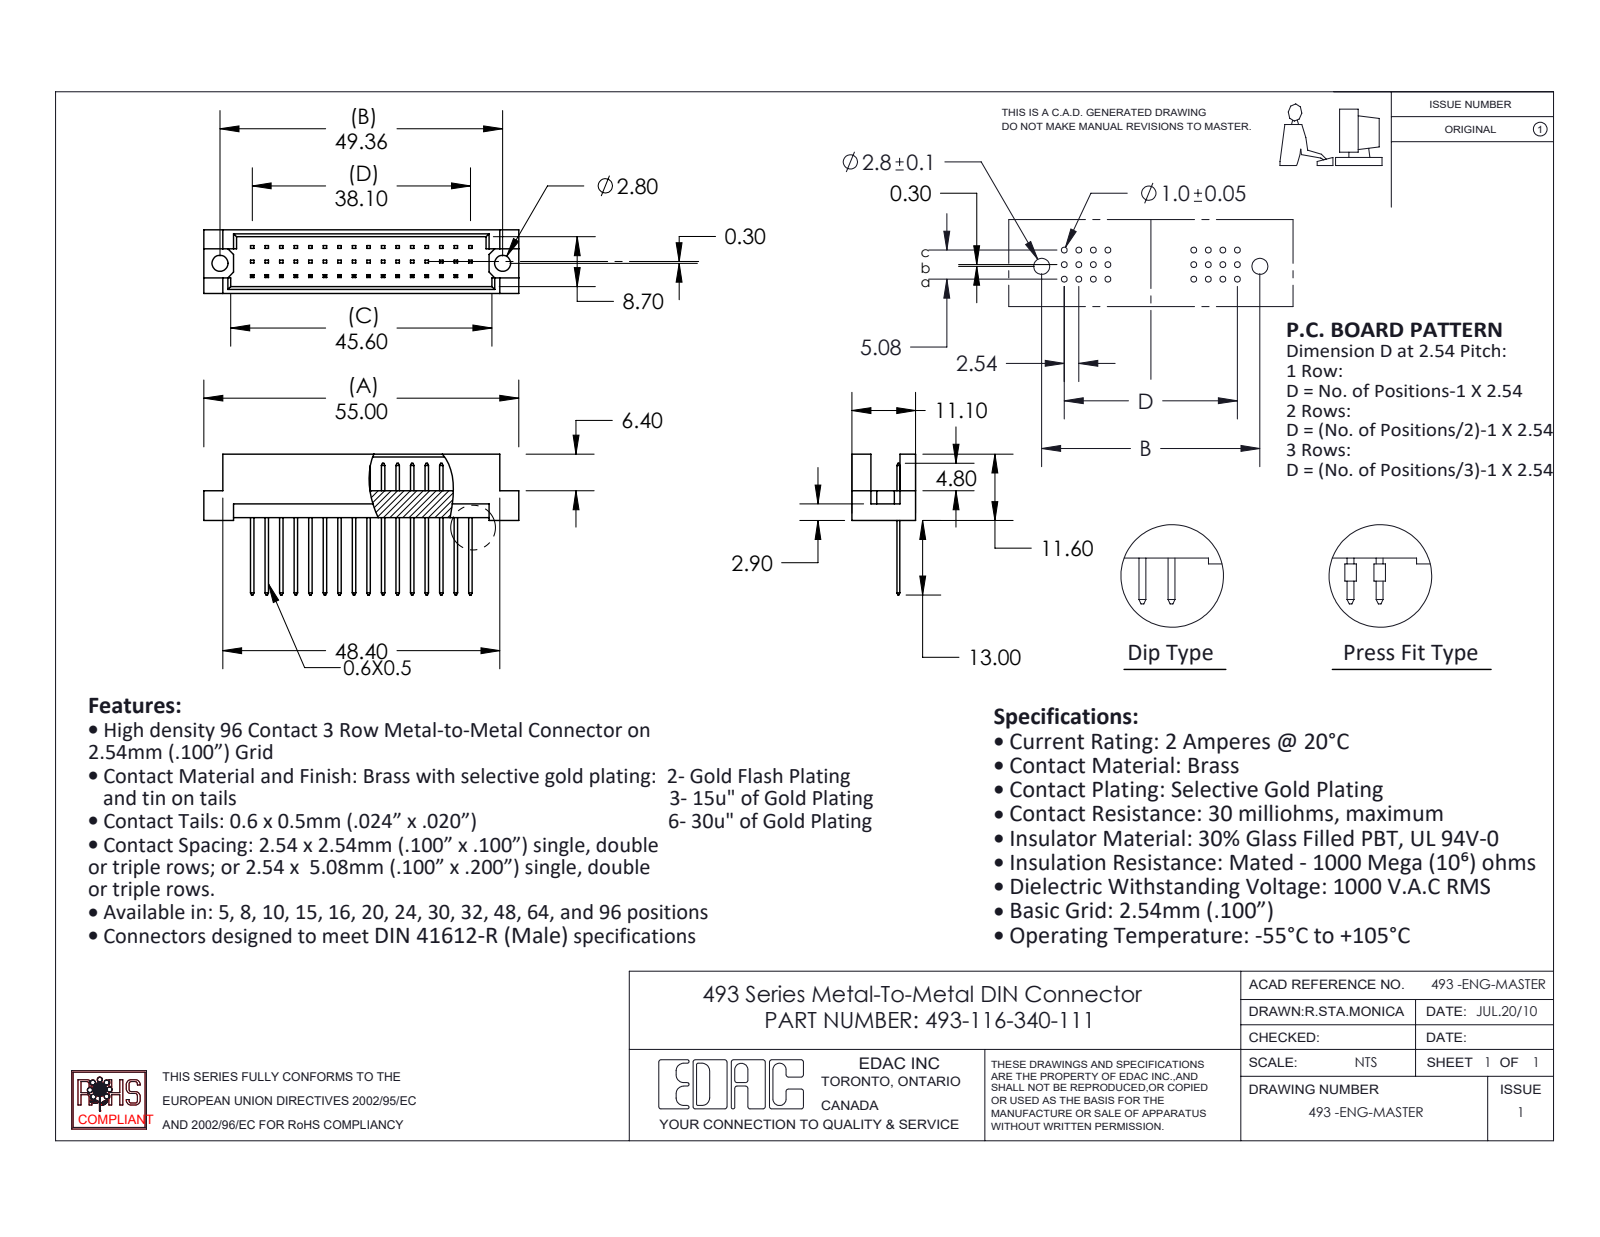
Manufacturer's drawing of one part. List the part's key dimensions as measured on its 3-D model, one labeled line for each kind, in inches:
Part name (STEP PRODUCT): 493 Part_48; 493-116-340-112; 493-290_40
STEP written by: SolidWorks 2020 (CONFIG_CONTROL_DESIGN)
Units: inches
Bodies: 17 solids, 468 faces (464 planar, 4 cylindrical, 0 other)
Overall size (bounding box): 2.165 × 0.969 × 0.437
Volume: 0.206 in³ · Surface area: 7.068 in²
Round holes (diameter × count): ⌀0.11 ×2
Main face-to-face distances: 0.047, 0.39, 0.437, 0.02, 0.343, 0.1, 0.185, 0.2, 0.109, 0.328
Hole centre spacings: 1.943
